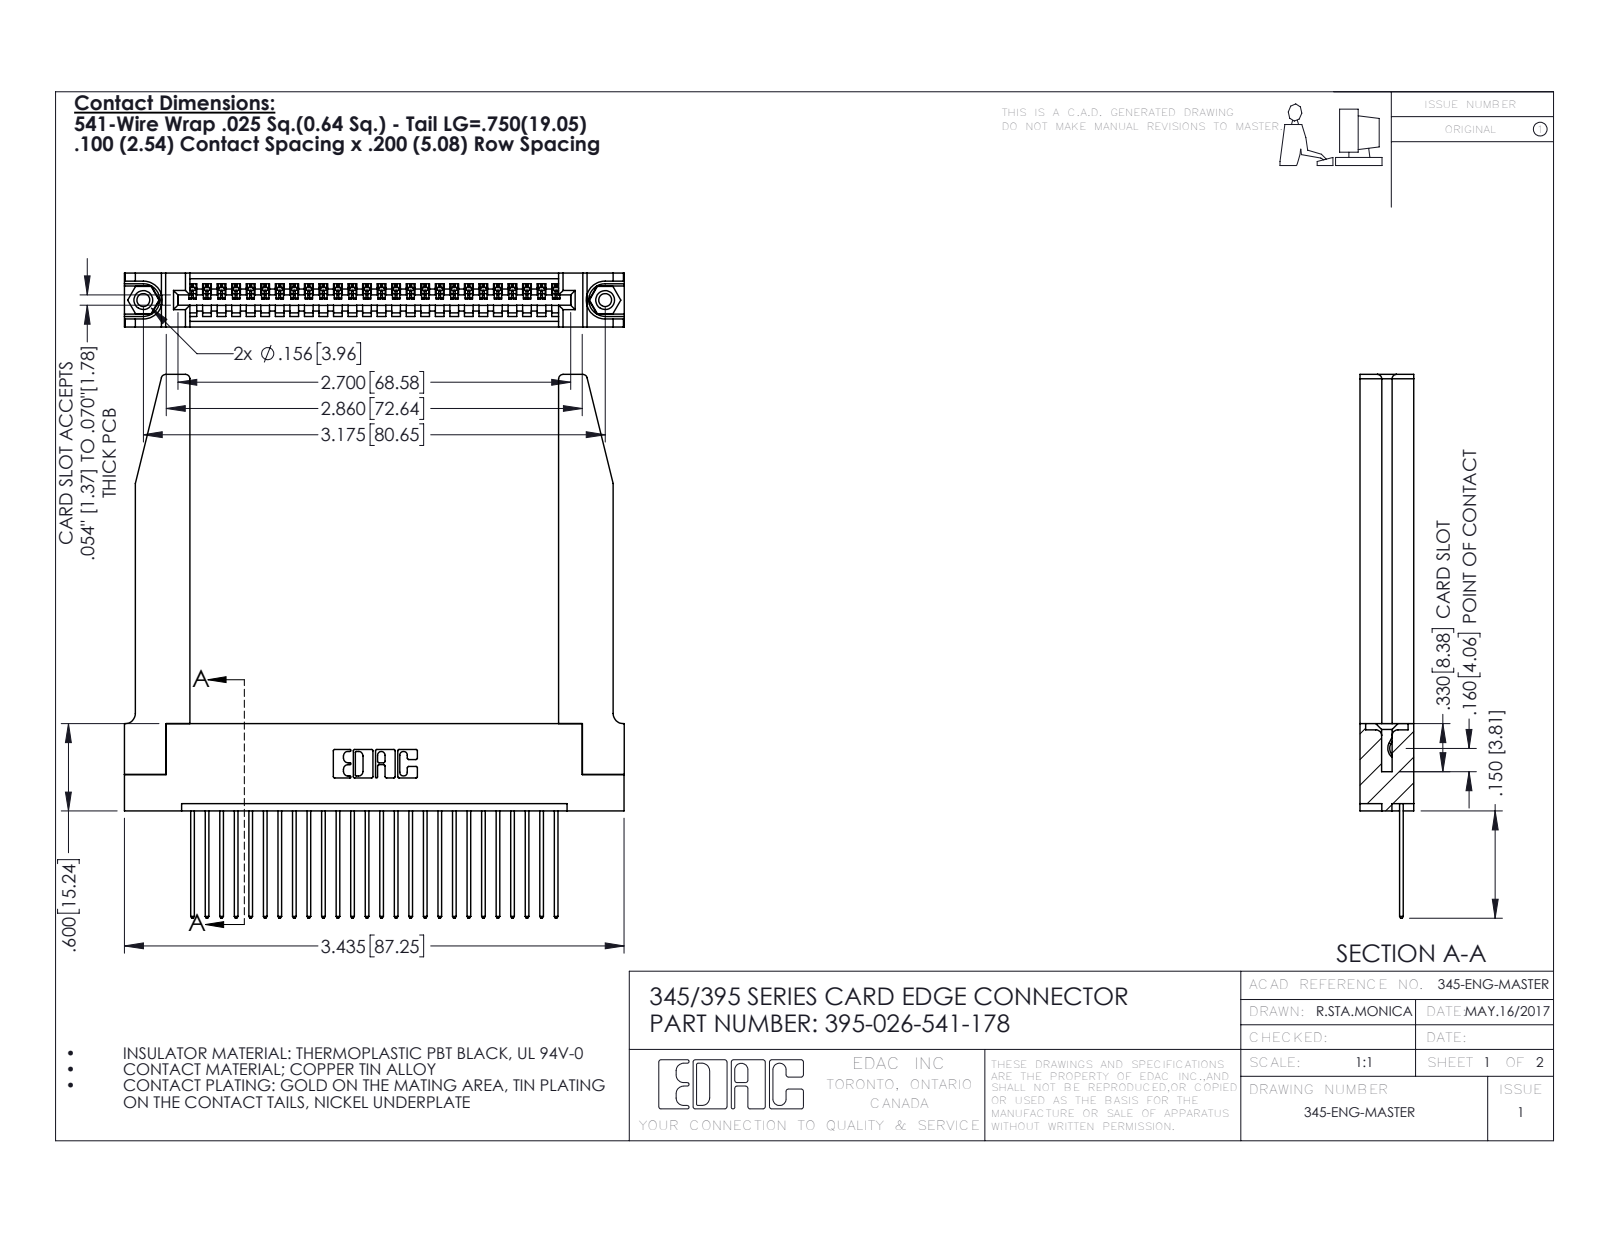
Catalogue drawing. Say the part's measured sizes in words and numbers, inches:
The part is named "345-220-078_345-220-078; 345-250-001_345-250-001-102; 345 Part_Flush Mounting Lugs - 0.156 Dia-TH; 395-026-541-178 (+1 more)". Its 3-D file was written by "SolidWorks 2016 (CONFIG_CONTROL_DESIGN)". It is 31 solids with 1868 faces: 1262 planar, 554 cylindrical and 52 other. Overall it measures 3.737 by 3.436 by 0.37 inches. Its volume is 0.977 cubic inches and its surface area 28.04 square inches. Round holes: 2 of diameter 0.089, 2 of diameter 0.125, 2 of diameter 0.156, 1 of diameter 0.064. Round bosses or shafts: 2 of diameter 0.155. Partial cylindrical surfaces (rounded edges, fillets, slot ends): 52 of radius 0.006, 52 of radius 0.01, 22 of radius 0.01, 8 of radius 0.03, 6 of radius 0.007, 6 of radius 0.031, 3 of radius 0.026, 2 of radius 0.031. The main face-to-face distances are 0.37, 0.072, 0.298, 0.2, 0.098, 0.272, 0.025, 0.148, 0.15, 0.225. The hole center spacings are 0.27, 2.94, 3.175.
